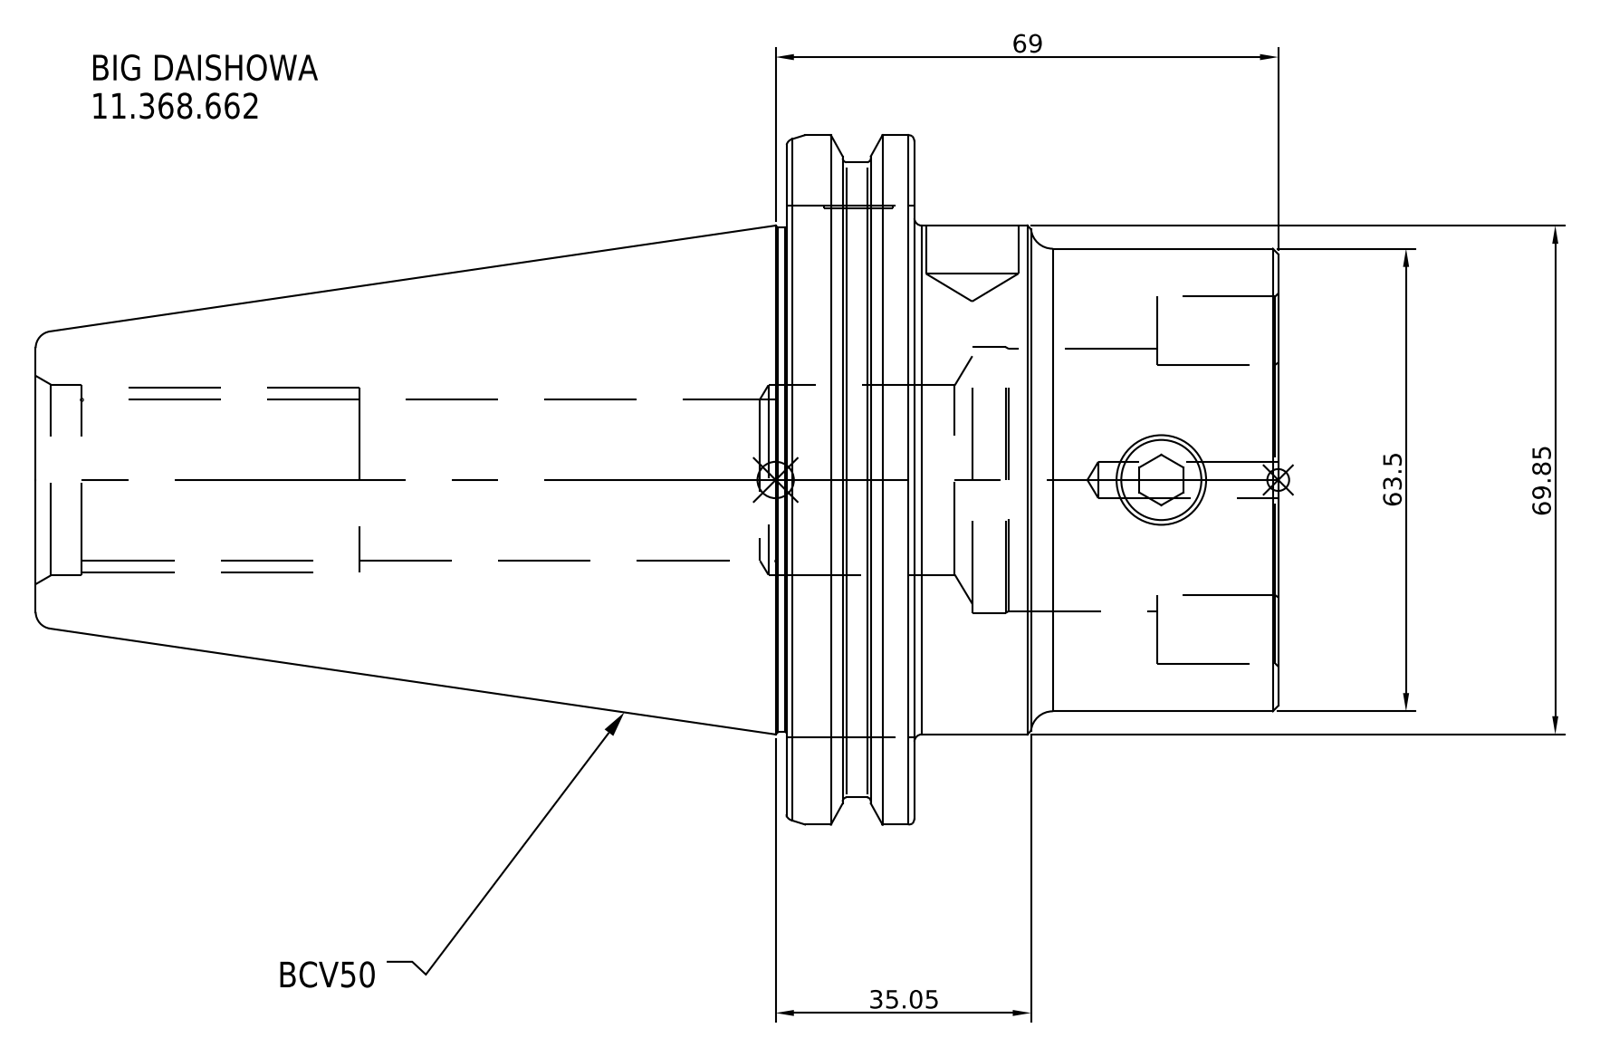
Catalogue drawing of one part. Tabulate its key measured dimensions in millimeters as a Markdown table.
| quantity | value |
| --- | --- |
| part name | 11.368.662 |
| STEP written by | SolidWorks 2021 (CONFIG_CONTROL_DESIGN) |
| units | millimeters |
| bodies | 1 solid, 16 faces (7 planar, 6 cylindrical, 3 other) |
| overall size | 170.6 × 98.43 × 98.43 |
| volume | 550 156 mm³ |
| surface area | 47 756 mm² |
| round bosses / shafts (diameter × count) | 98.43 × 1, 91.29 × 1, 69.85 × 1, 63.5 × 1 |
| main face-to-face distances | 17.55, 49.95, 67.5, 170.6, 120.65, 103.1, 34, 15.95, 33.5, 136.6 |
